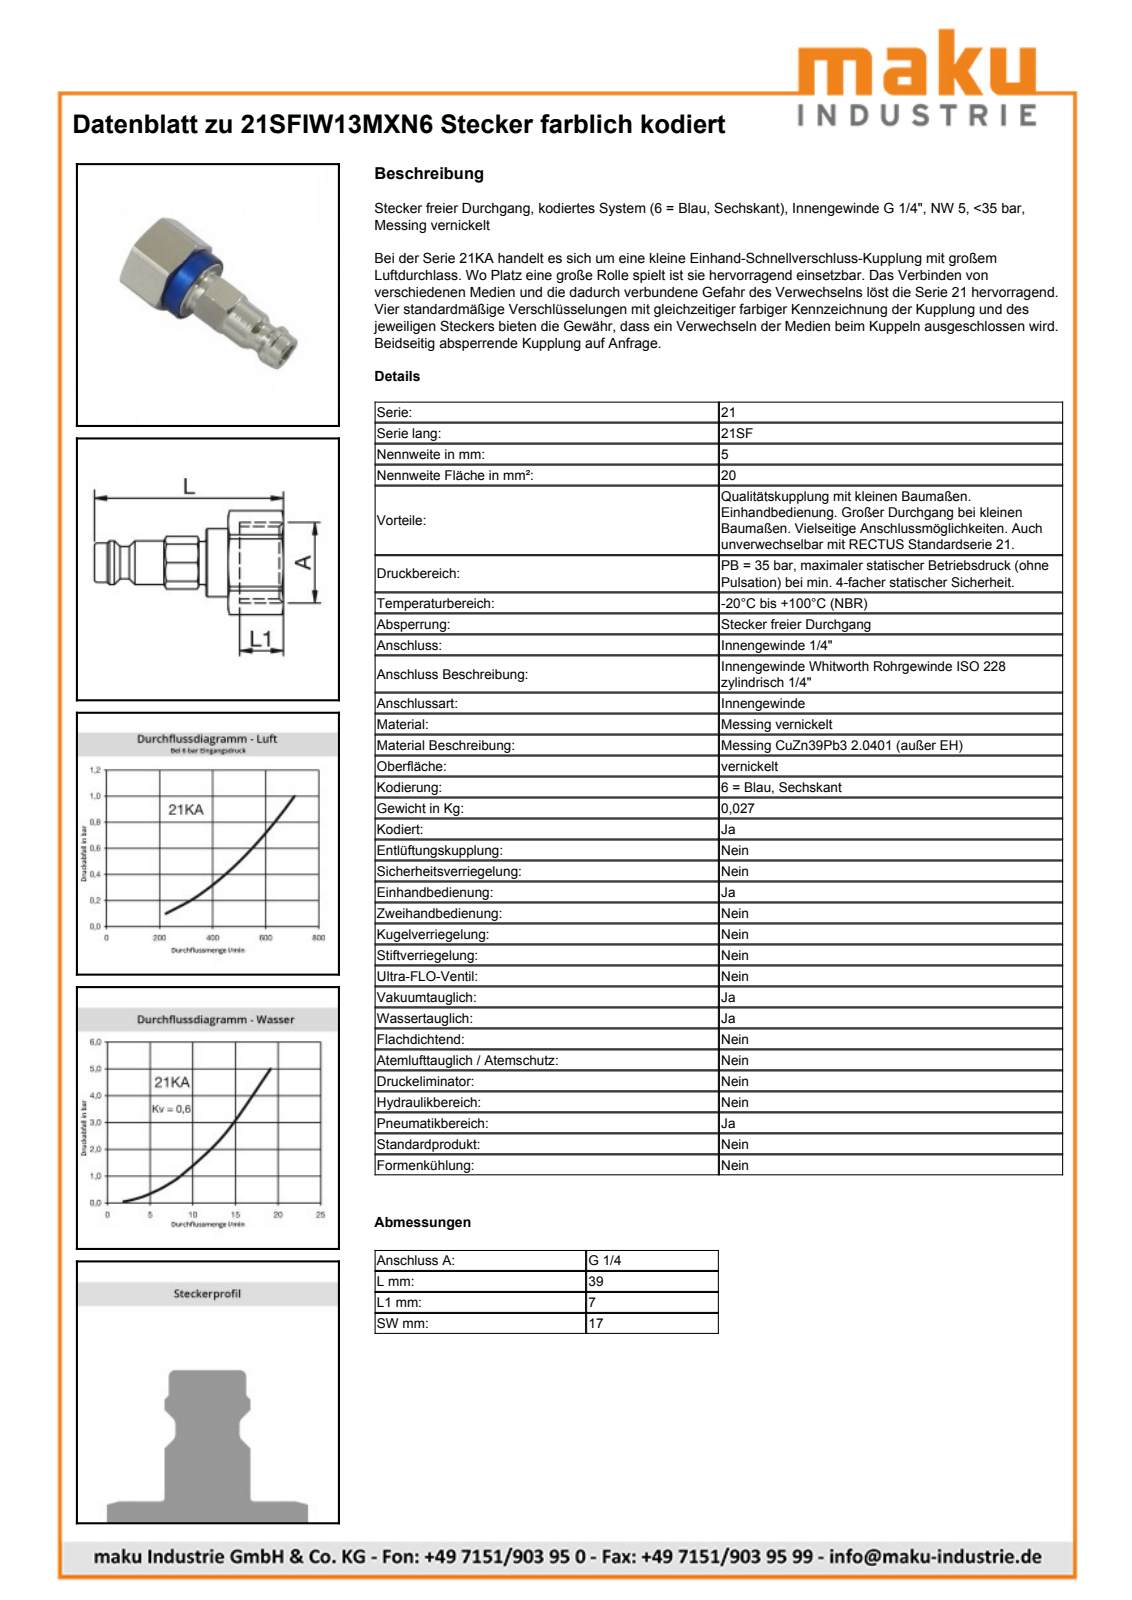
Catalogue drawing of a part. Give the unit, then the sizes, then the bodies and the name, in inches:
Units: inches
Overall size (bounding box): 1.535 × 0.754 × 0.669
Round holes (diameter × count): ⌀0.195 ×1, ⌀0.451 ×1, ⌀0.545 ×1, ⌀0.553 ×1
Round bosses / shafts (diameter × count): ⌀0.61 ×1, ⌀0.551 ×1, ⌀0.382 ×1, ⌀0.354 ×1, ⌀0.319 ×1, ⌀0.262 ×1
Partial cylindrical surfaces — rounded edges, fillets, slot ends (radius × count): R0.224 ×1, R0.377 ×1
Main face-to-face distances: 0.669, 0.138, 0.531, 0.394, 0.433, 0.079, 0.354, 0.177, 0.256, 0.61
Volume: 0.221 in³ · Surface area: 4.954 in²
Bodies: 2 solids, 68 faces (19 planar, 23 cylindrical, 26 other)
Part name (STEP PRODUCT): D111679; D111676; D103012
STEP written by: Autodesk Inventor 2013 (AUTOMOTIVE_DESIGN)
